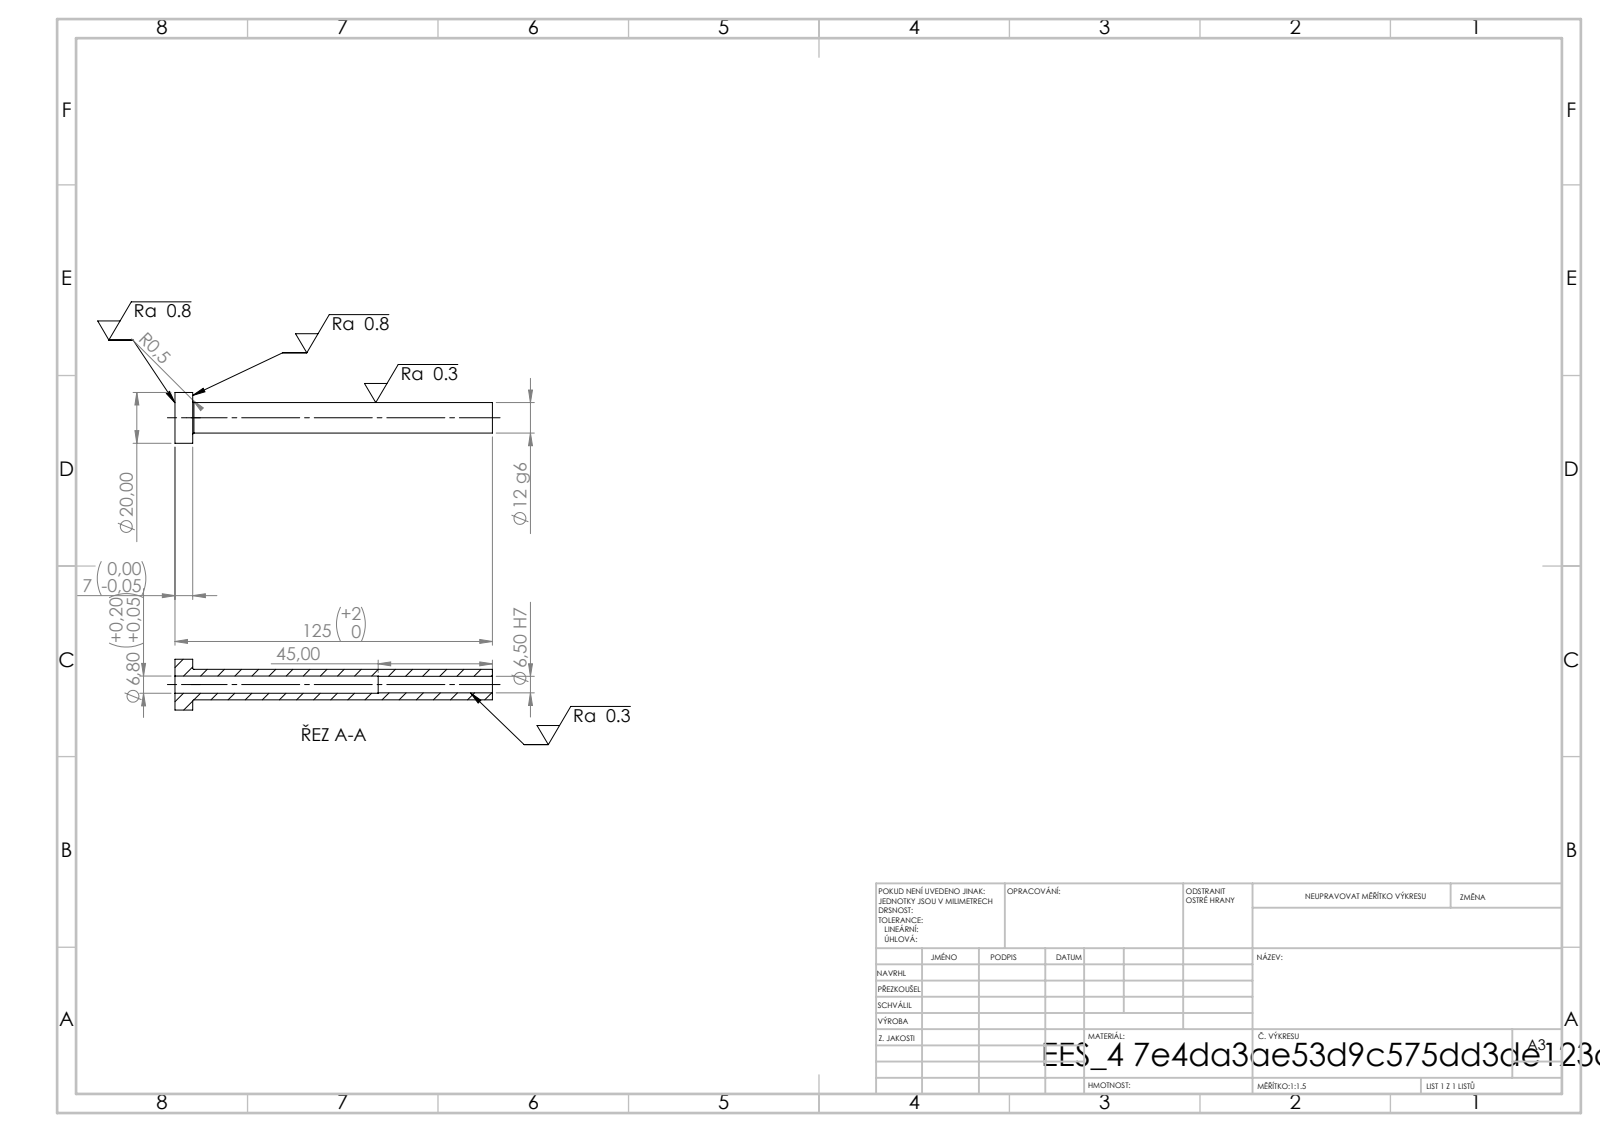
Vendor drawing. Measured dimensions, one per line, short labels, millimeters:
written by: SolidWorks 2019 (CONFIG_CONTROL_DESIGN)
unit: mm
bodies: 1 solid, 14 faces (4 planar, 8 cylindrical, 2 other)
size: 125 × 20 × 20
volume: 11 148 mm³; area: 8 070 mm²
holes: 1× ⌀6.5, 1× ⌀6.8
bosses: 1× ⌀20, 1× ⌀12
face distances: 7, 125, 118, 80, 73, 45
